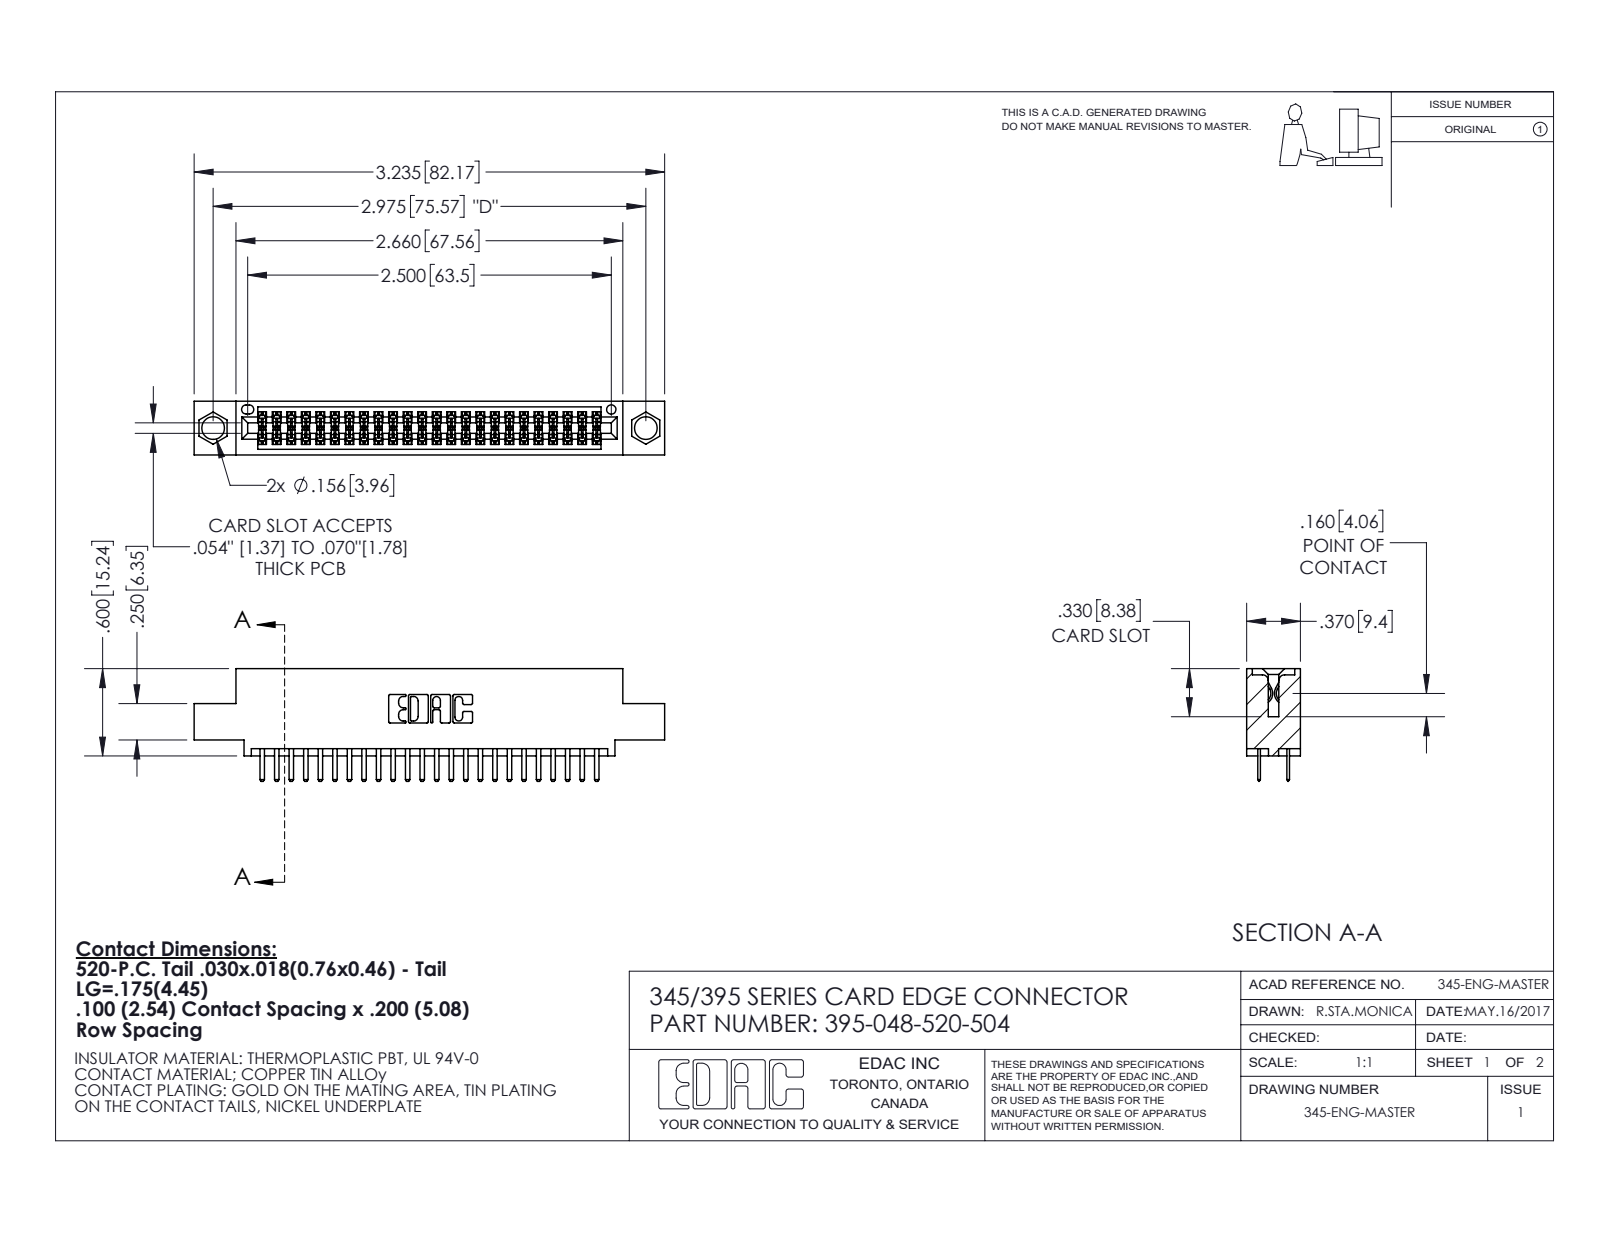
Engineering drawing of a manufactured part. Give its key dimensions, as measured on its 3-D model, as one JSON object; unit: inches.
{"part_name": "395-048-520-504; 345-292-001_345-293-120; 345 Part_0.110 Offset - 0.156 Dia-TI", "step_written_by": "SolidWorks 2020 (CONFIG_CONTROL_DESIGN)", "units": "inches", "bodies": {"solids": 49, "faces": 2736, "planar": 1778, "cylindrical": 958, "other": 0}, "overall_size": [3.235, 0.775, 0.37], "volume_in3": 0.465, "surface_area_in2": 16.75, "round_holes": [[0.156, 2], [0.064, 1]], "partial_cylinders_radius": [[0.006, 72], [0.01, 52], [0.01, 22], [0.007, 6], [0.031, 6], [0.026, 3], [0.014, 2], [0.019, 2]], "face_to_face_distances": [0.072, 0.298, 0.2, 0.37, 0.098, 0.272, 0.025, 0.225, 0.022, 0.072], "hole_center_spacings": [0.27, 2.741, 2.975]}
